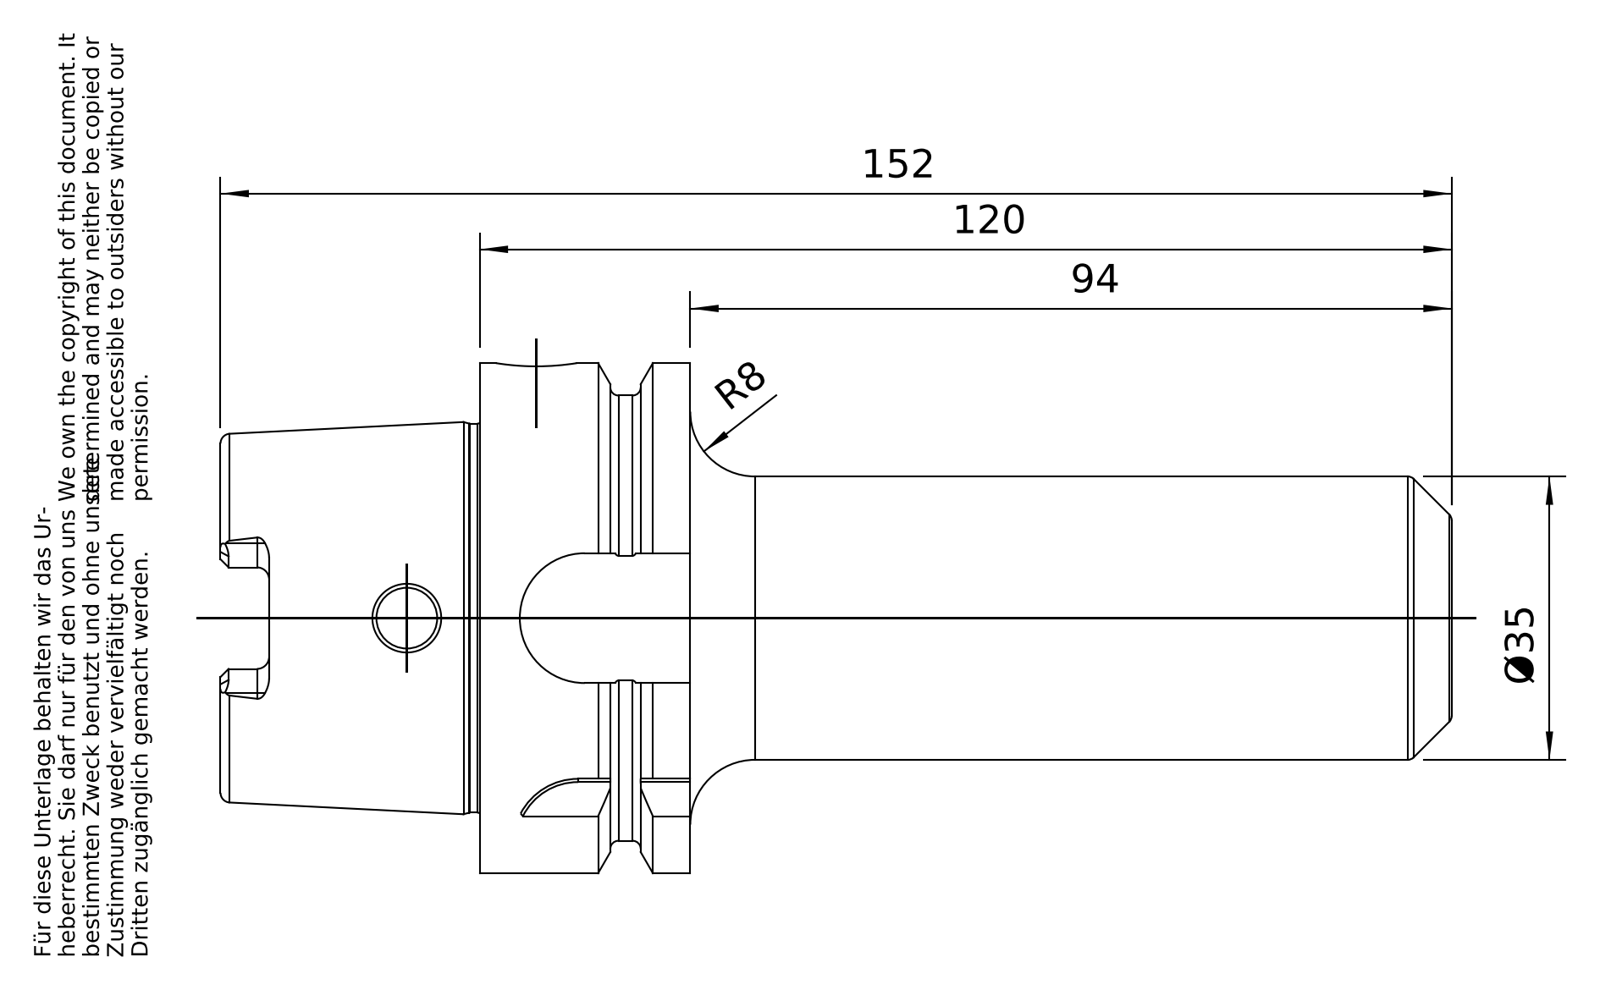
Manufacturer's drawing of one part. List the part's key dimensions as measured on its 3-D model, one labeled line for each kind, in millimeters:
Part name (STEP PRODUCT): A63-120-02
STEP written by: PRO/ENGINEER BY PARAMETRIC TECHNOLOGY CORPORATION, 2010430 (CONFIG_CONTROL_DESIGN)
Units: millimetres
Bodies: 1 solid, 177 faces (57 planar, 48 cylindrical, 72 other)
Overall size (bounding box): 152 × 63 × 63
Volume: 157 296 mm³ · Surface area: 35 756 mm²
Round holes (diameter × count): ⌀7.5 ×1, ⌀10 ×1, ⌀16.72 ×1, ⌀16.92 ×1, ⌀18.32 ×1, ⌀18.66 ×1, ⌀34 ×1, ⌀40 ×1
Round bosses / shafts (diameter × count): ⌀63 ×1, ⌀55 ×1, ⌀48.04 ×1, ⌀35 ×1, ⌀18 ×1
Partial cylindrical surfaces — rounded edges, fillets, slot ends (radius × count): R1.5 ×6, R3 ×4, R8 ×1, R8.02 ×1, R9.02 ×1
Main face-to-face distances: 26, 10, 52.8, 16, 32, 42, 58, 53.8, 21.8, 11.8
